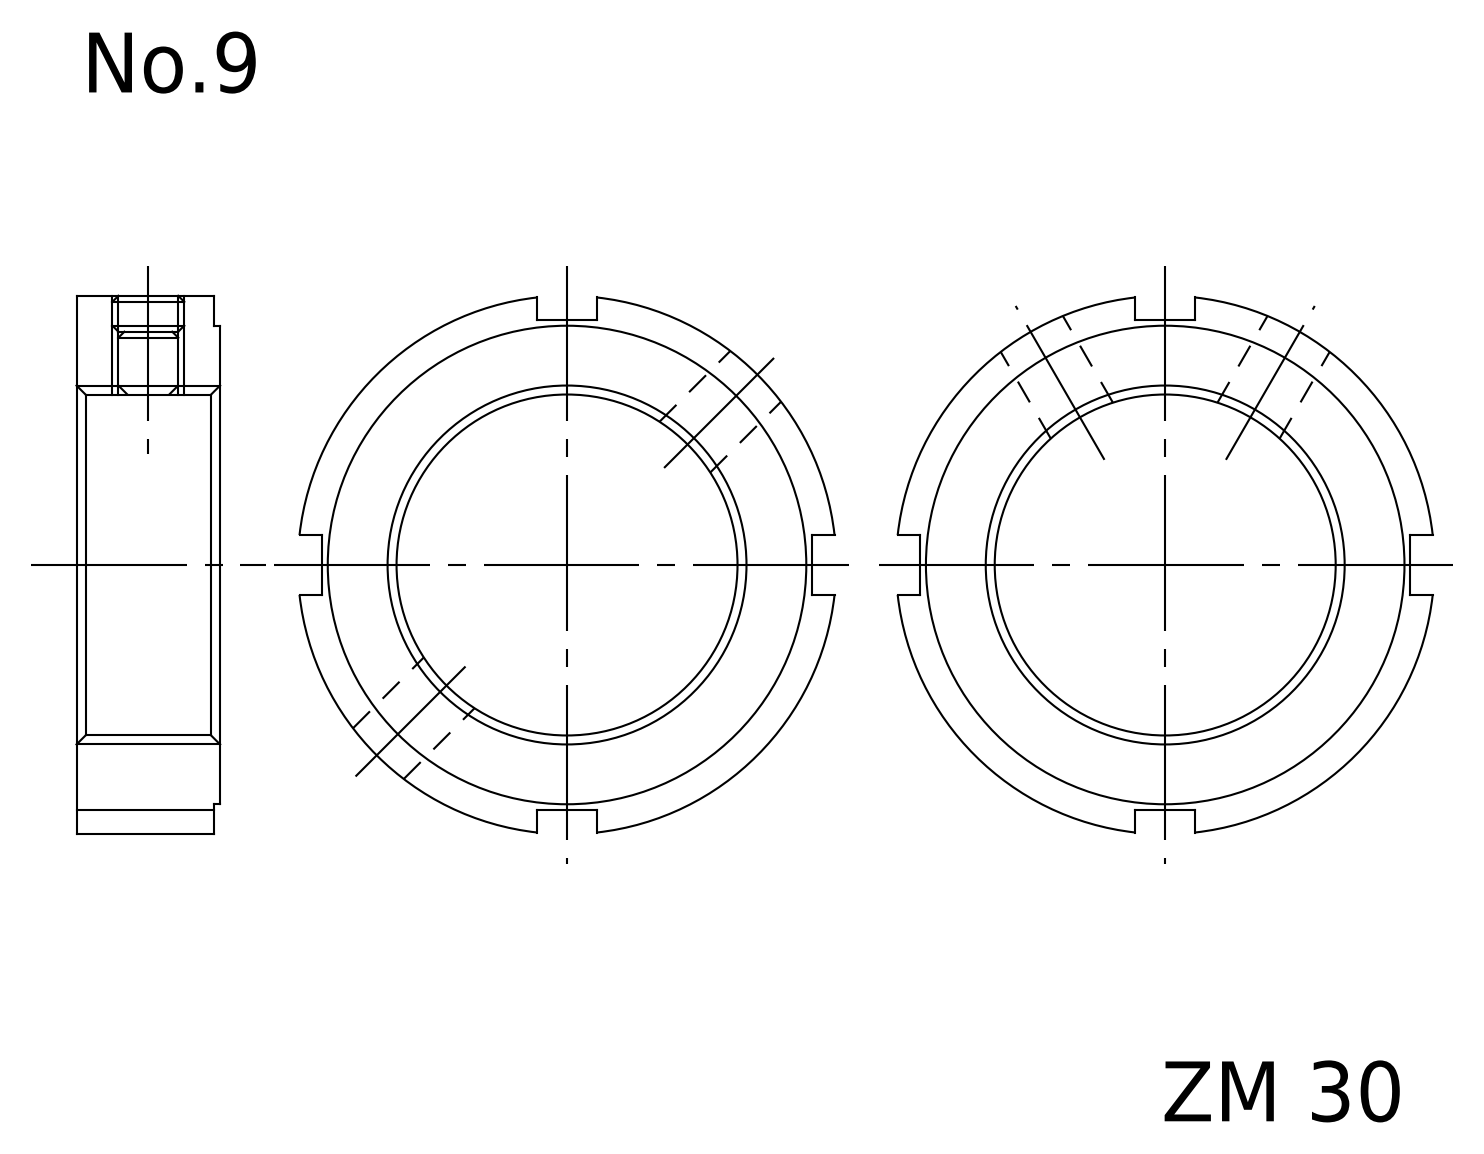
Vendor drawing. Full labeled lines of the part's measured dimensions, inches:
Part name (STEP PRODUCT): FKD ZM 30
STEP written by: Autodesk Inventor 2011 (AUTOMOTIVE_DESIGN)
Units: inches
Bodies: 1 solid, 23 faces (15 planar, 8 cylindrical, 0 other)
Overall size (bounding box): 1.761 × 1.761 × 0.472
Volume: 0.592 in³ · Surface area: 7.496 in²
Round holes (diameter × count): ⌀0.194 ×2, ⌀1.181 ×1
Round bosses / shafts (diameter × count): ⌀1.772 ×1, ⌀1.575 ×1
Main face-to-face distances: 0.472, 0.02, 0.453, 0.709, 0.906, 1.614, 0.197
